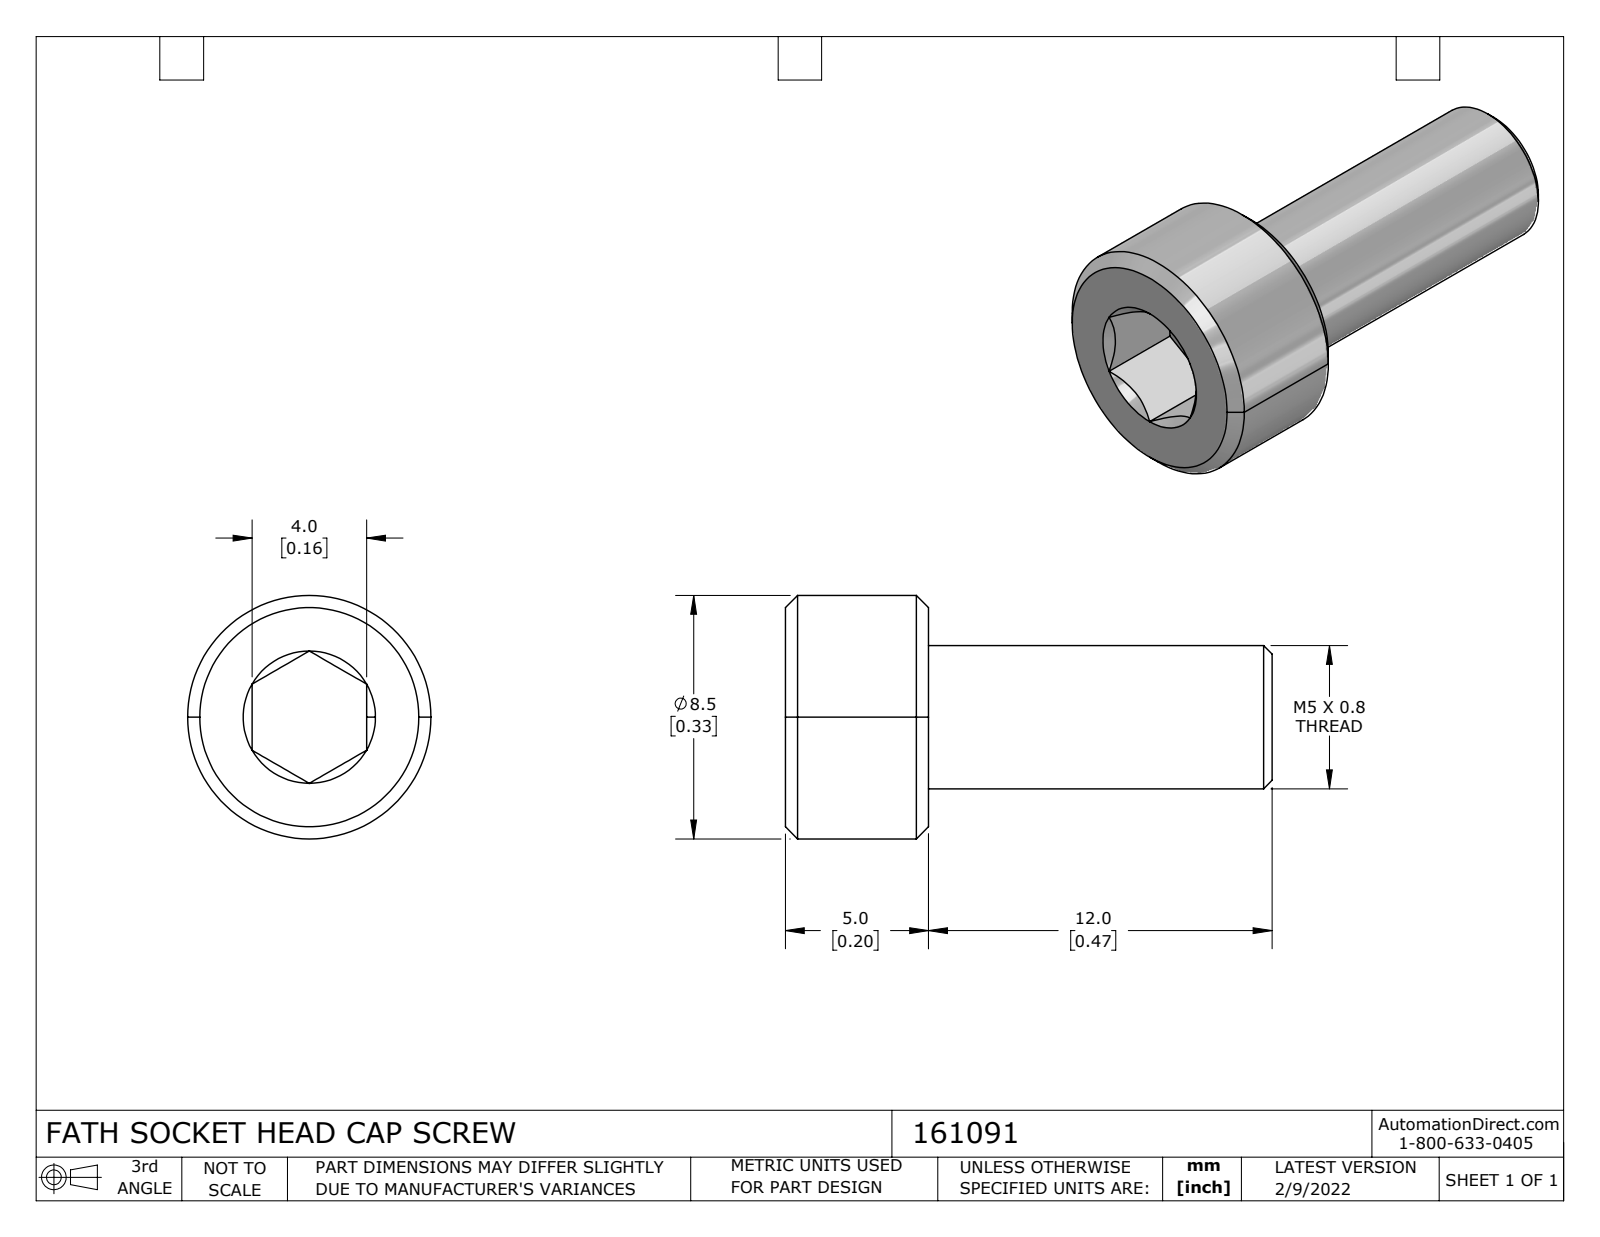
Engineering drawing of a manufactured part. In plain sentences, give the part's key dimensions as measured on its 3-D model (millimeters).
The part is named "161091". Its 3-D file was written by "SolidWorks 2021 (CONFIG_CONTROL_DESIGN)". It is 1 solid with 27 faces: 10 planar, 4 cylindrical and 13 other. Overall it measures 17 by 8.5 by 8.5 millimeters. Its volume is 472 cubic millimeters and its surface area 459 square millimeters. Round bosses or shafts: 1 of diameter 8.5, 1 of diameter 5. The main face-to-face distances are 5, 4, 17, 12, 3, 2, 14.
